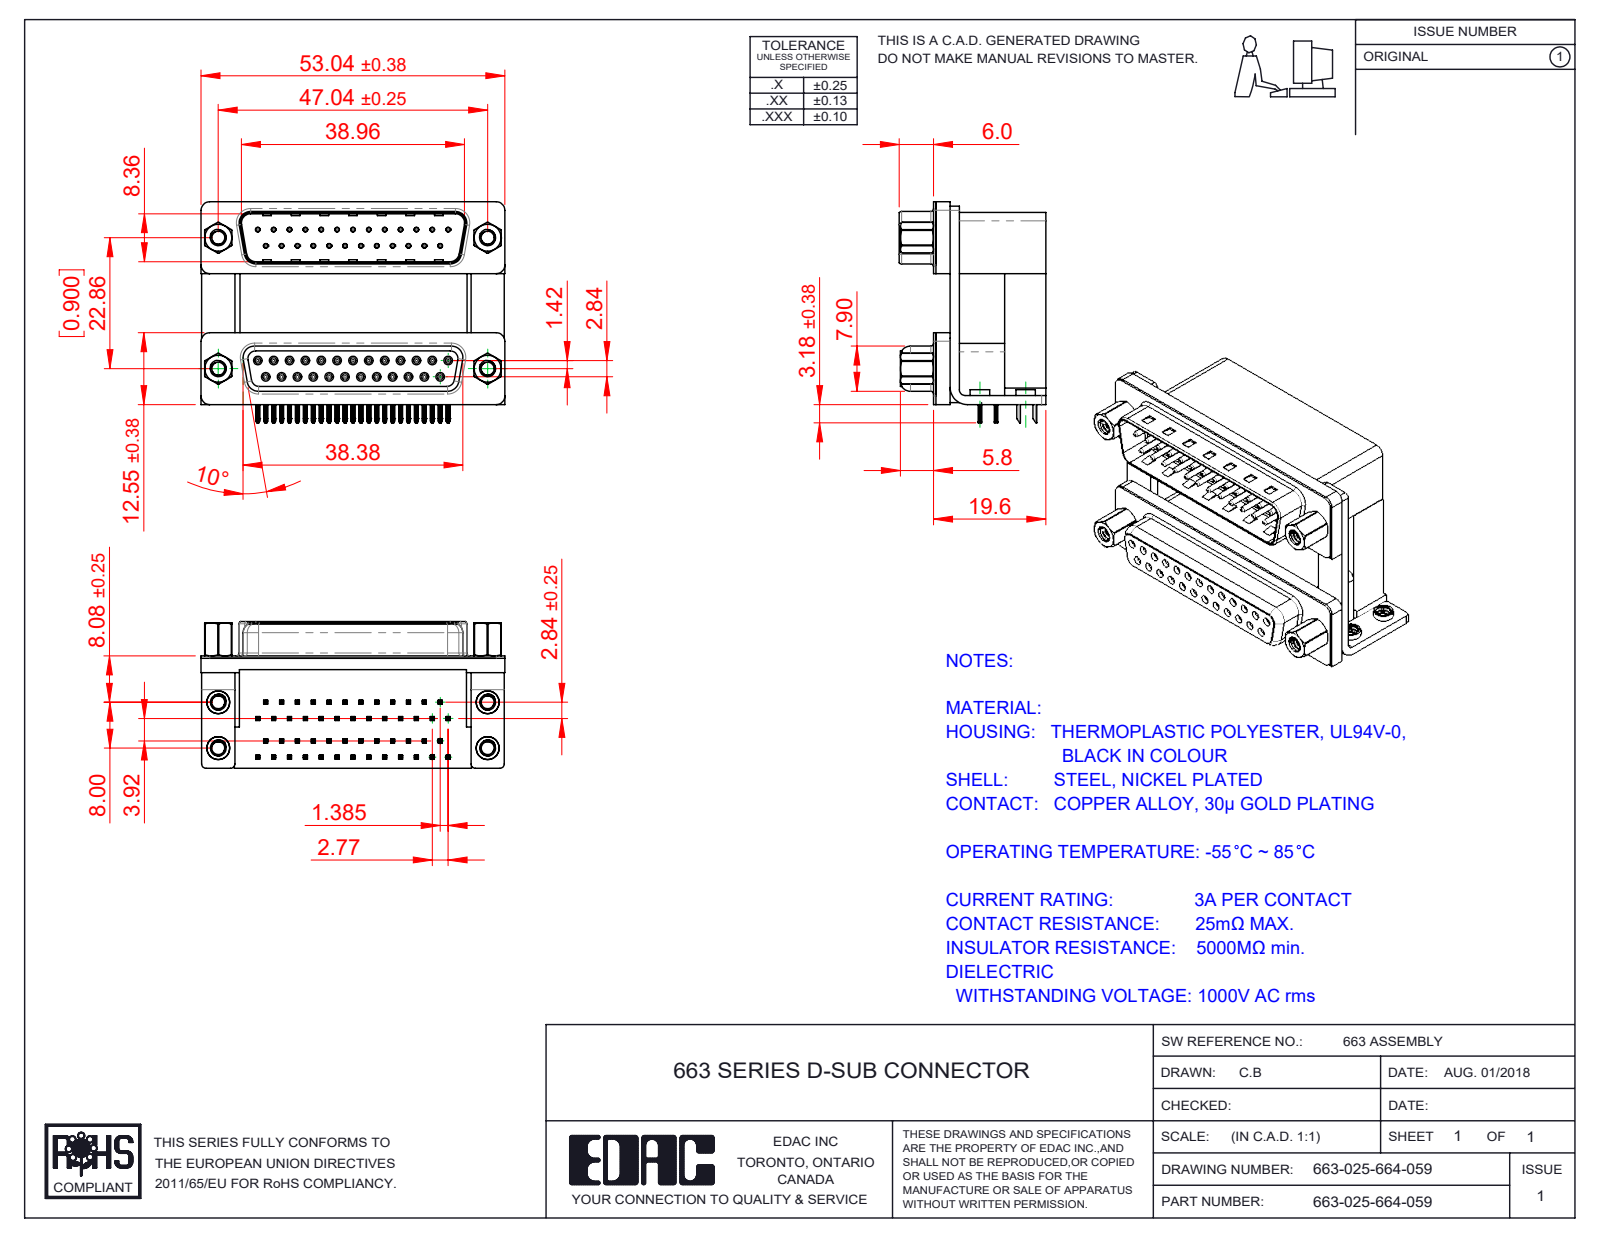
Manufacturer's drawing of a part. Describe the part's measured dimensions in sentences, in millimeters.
The part is named "663 4-40 Hex Standoff 5; 663 Contact Bottom Lower; 663-025-664-059; 663 Contact Top Lower (+8 more)". Its 3-D file was written by "SolidWorks 2020 (CONFIG_CONTROL_DESIGN)". It is 69 solids with 6595 faces: 3313 planar, 1763 cylindrical and 1519 other. Overall it measures 53.04 by 38.59 by 25.6 millimeters. Its volume is 24 176 cubic millimeters and its surface area 26 152 square millimeters. Round holes: 50 of diameter 0.8, 25 of diameter 0.35, 25 of diameter 0.9, 8 of diameter 2.26, 4 of diameter 2.29, 4 of diameter 2.75, 4 of diameter 3.2, 4 of diameter 3.5, 4 of diameter 4, 4 of diameter 4.8, 4 of diameter 5. Round bosses or shafts: 25 of diameter 1.2, 25 of diameter 0.75, 4 of diameter 4.9, 4 of diameter 4.75, 4 of diameter 4, 4 of diameter 3.9, 4 of diameter 3.4, 4 of diameter 2.79. Partial cylindrical surfaces (rounded edges, fillets, slot ends): 200 of radius 0.1, 100 of radius 0.15, 100 of radius 0.25, 50 of radius 0.12, 50 of radius 0.35, 25 of radius 0.34, 14 of radius 1.5, 12 of radius 0.28. The main face-to-face distances are 19.2, 12, 0.4, 7.2, 10.7, 16.7, 9.5, 2.5, 12.4, 22.86. The hole center spacings are 3.16, 2.77, 5.54, 11.08, 8.31, 5.03, 13.85, 7.48.
